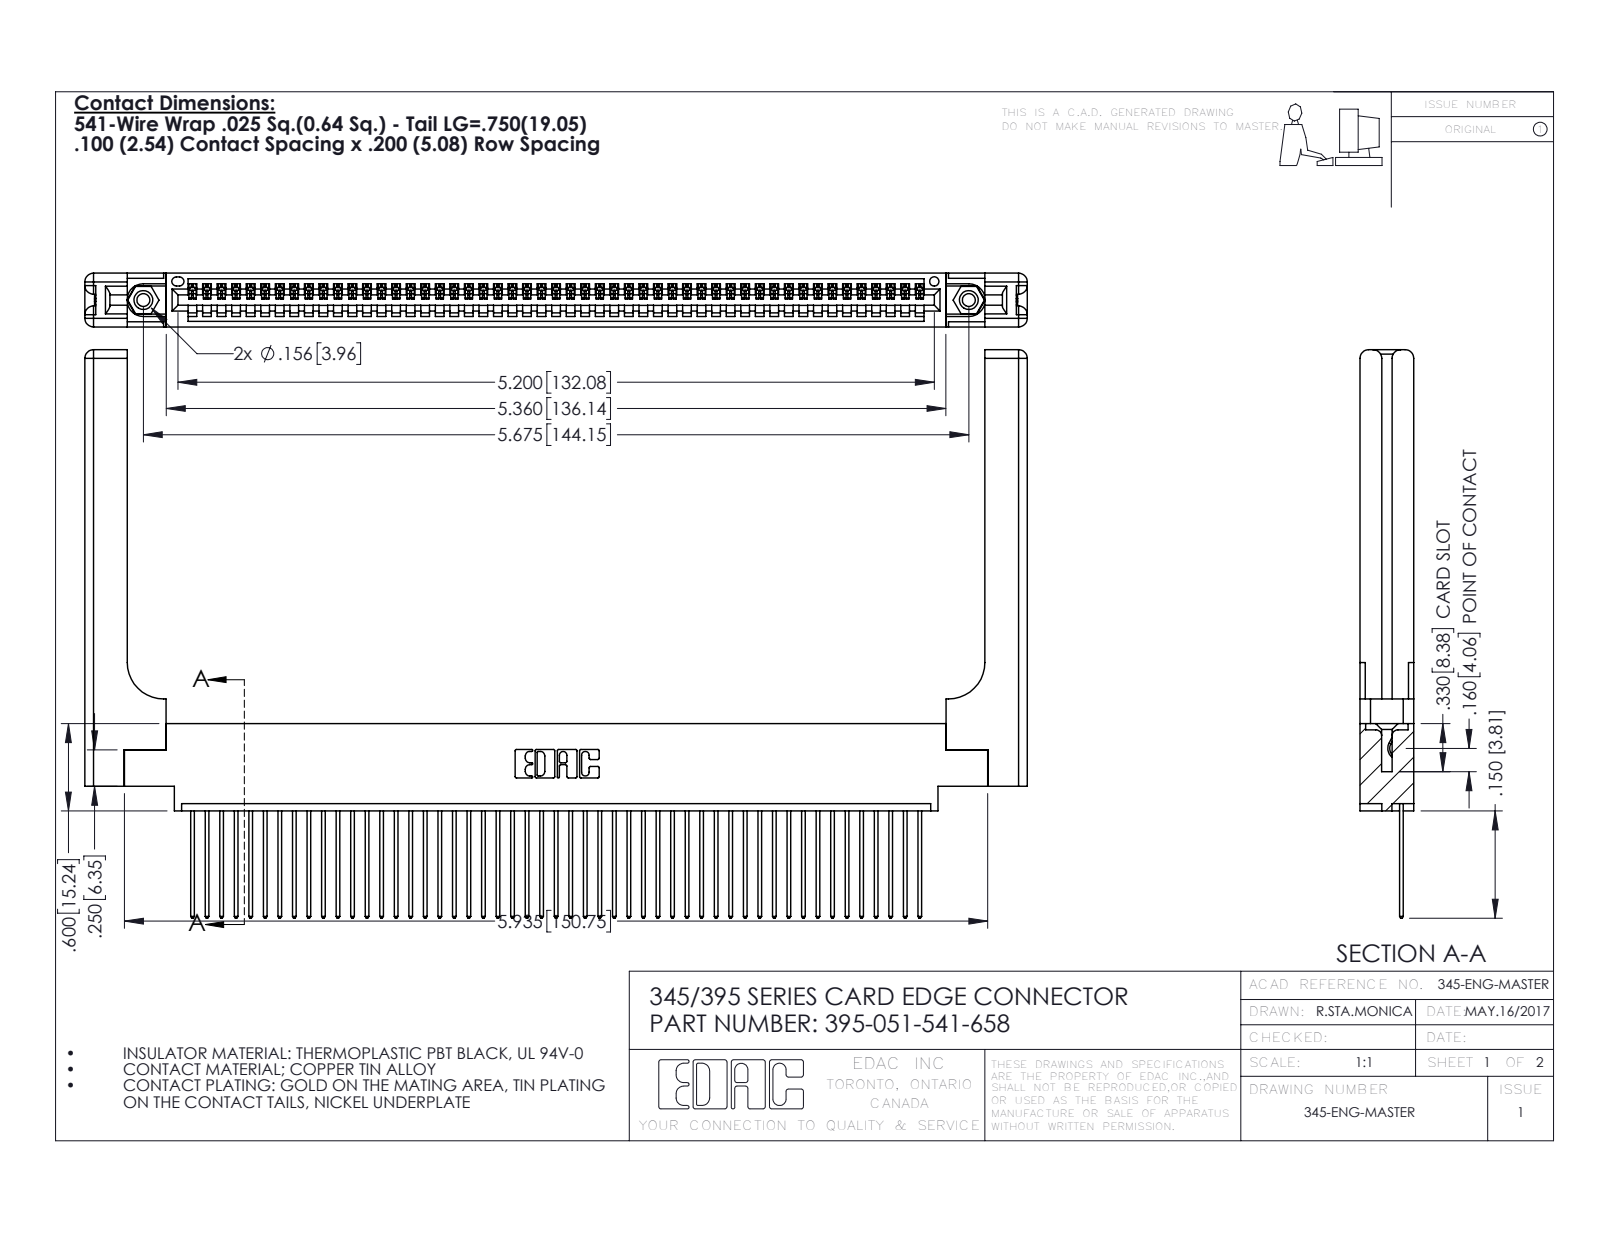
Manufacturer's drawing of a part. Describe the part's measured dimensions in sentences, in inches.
The part is named "345-250-001_345-250-001-102; 345-292-001_345-293-141; 345-220-058_345-220-058; 345 Part_0.170 Offset - 0.156 Dia-TH (+1 more)". Its 3-D file was written by "SolidWorks 2016 (CONFIG_CONTROL_DESIGN)". It is 56 solids with 3344 faces: 2272 planar, 1012 cylindrical and 60 other. Overall it measures 6.479 by 3.907 by 0.37 inches. Its volume is 1.481 cubic inches and its surface area 42.61 square inches. Round holes: 2 of diameter 0.089, 2 of diameter 0.125, 2 of diameter 0.156, 1 of diameter 0.064. Round bosses or shafts: 2 of diameter 0.155. Partial cylindrical surfaces (rounded edges, fillets, slot ends): 102 of radius 0.006, 102 of radius 0.01, 22 of radius 0.01, 16 of radius 0.06, 6 of radius 0.007, 6 of radius 0.031, 3 of radius 0.026, 2 of radius 0.03. The main face-to-face distances are 0.072, 0.37, 0.298, 0.098, 0.272, 0.025, 0.2, 0.225, 0.148, 0.15. The hole center spacings are 0.27, 5.439, 5.675.
